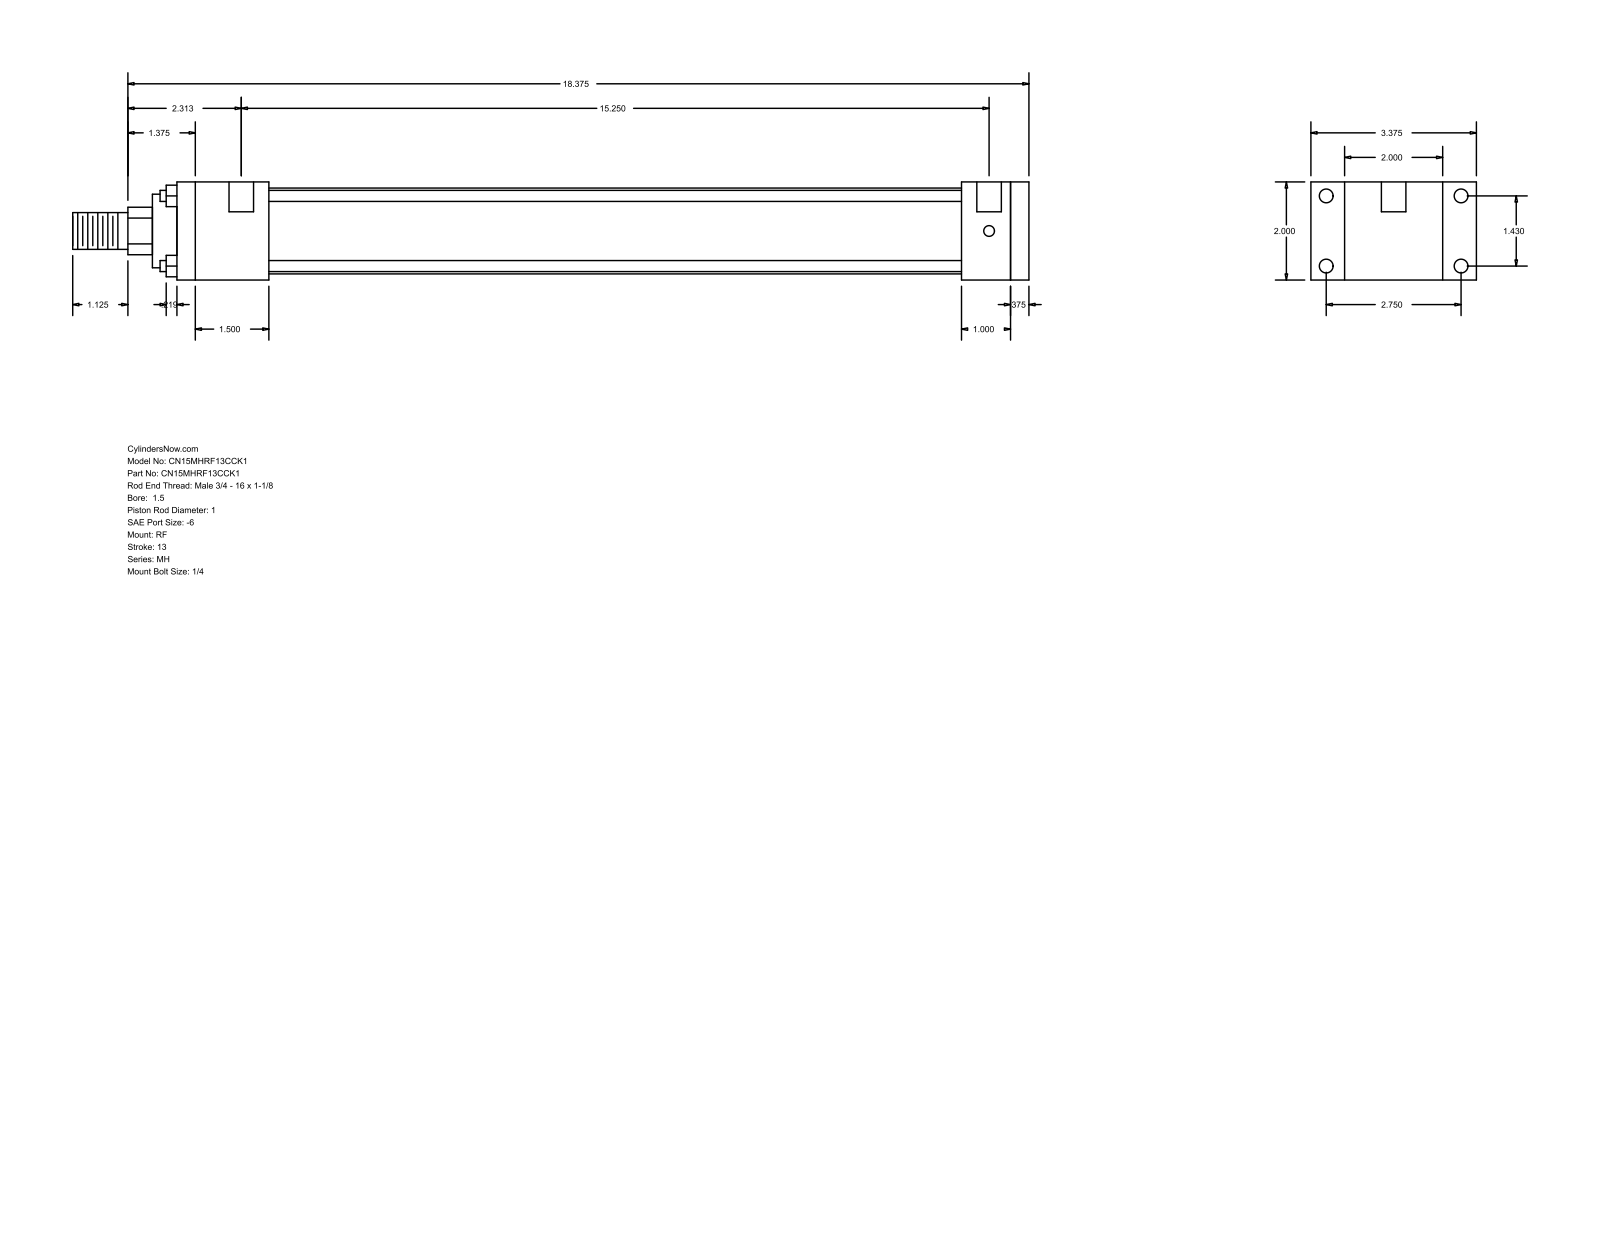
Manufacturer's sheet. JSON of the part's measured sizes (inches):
{"part_name": "MH_RF__0150_1", "step_written_by": "GSSL Pune (CONFIG_CONTROL_DESIGN)", "units": "inches", "bodies": {"solids": 0, "faces": 92, "planar": 64, "cylindrical": 28, "other": 0}, "overall_size": [19.5, 3.375, 2], "round_holes": [[0.219, 4], [0.281, 4], [0.5, 2]], "round_bosses_or_shafts": [[0.225, 4], [1.75, 1], [1.5, 1], [1, 1], [0.75, 1]], "partial_cylinders_radius": [[0.484, 1]], "face_to_face_distances": [2, 0.375, 17, 1, 17.375, 0.687, 2.687, 16, 1.375, 1.875], "hole_center_spacings": [1.43, 2.75, 3.099, 15.375, 0.125, 15.25]}
